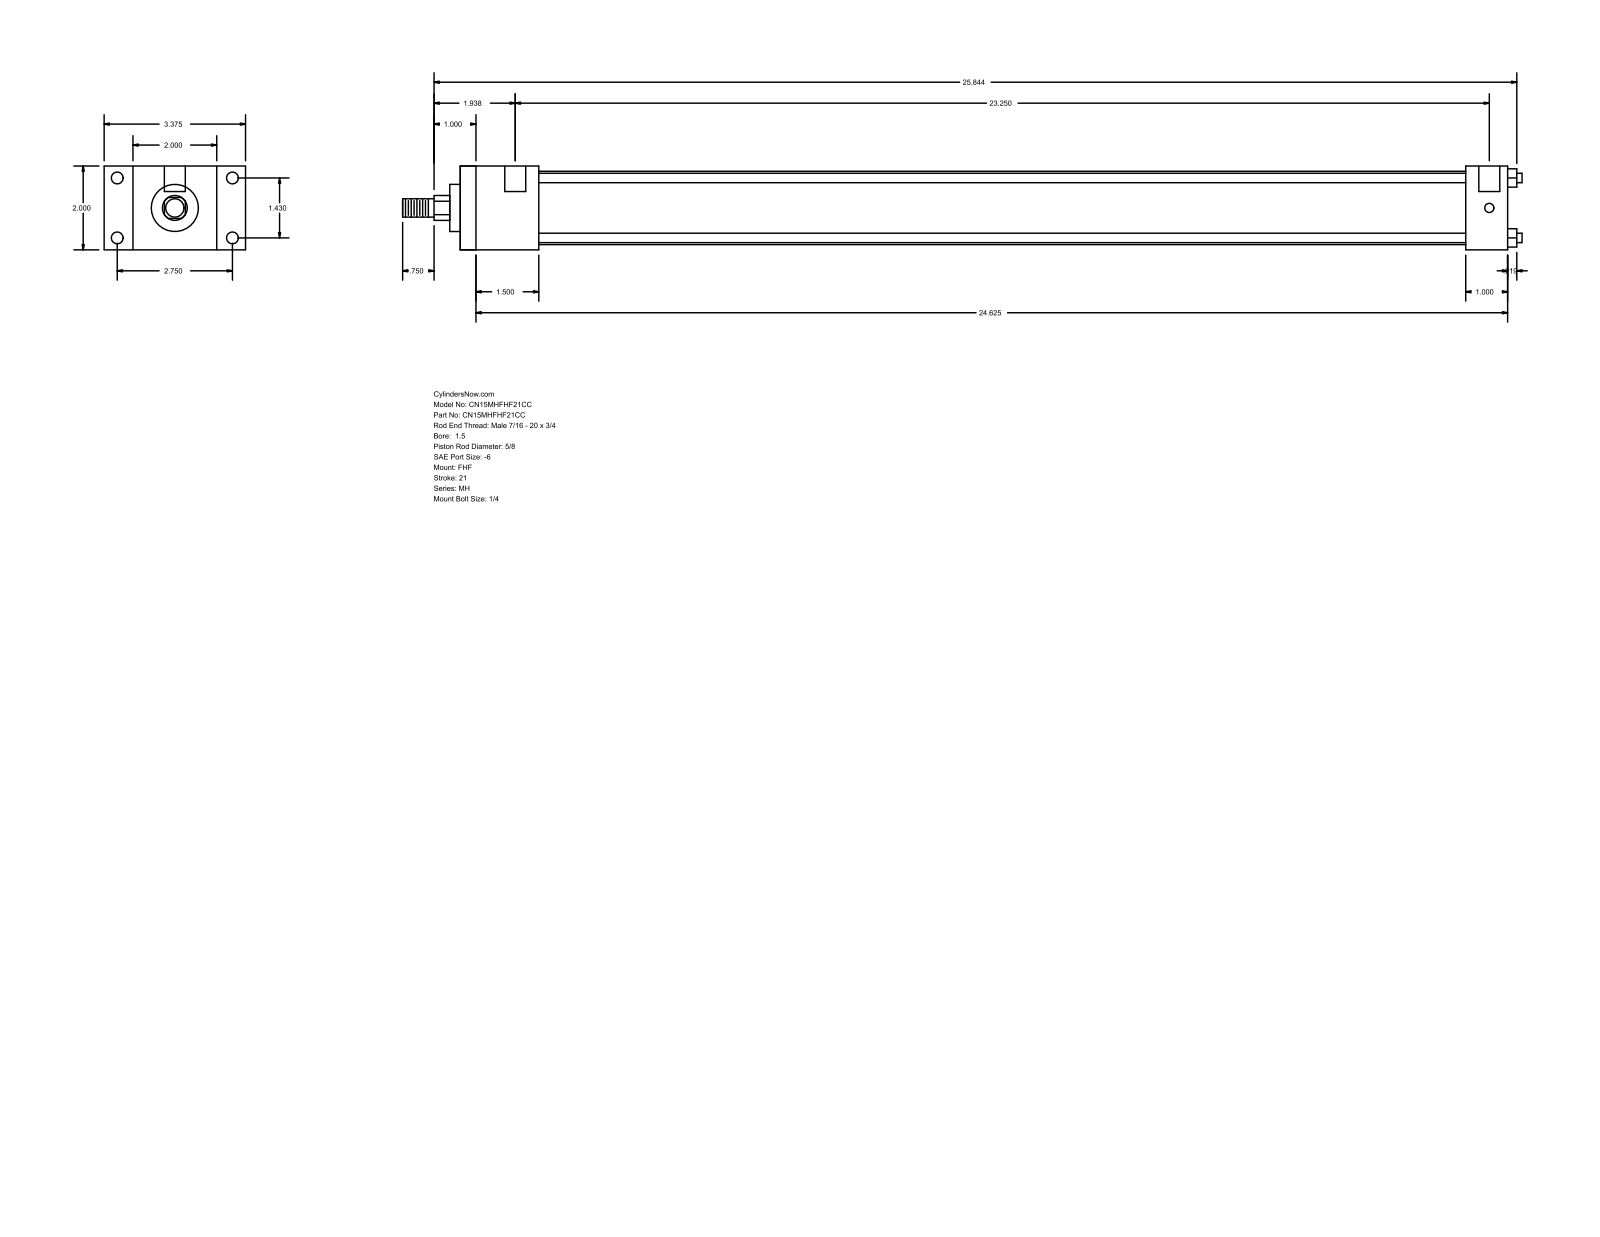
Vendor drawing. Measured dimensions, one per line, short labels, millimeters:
name: MH_FHF__0150_0.625
written by: GSSL Pune (CONFIG_CONTROL_DESIGN)
unit: mm
bodies: 0 solids, 88 faces (60 planar, 28 cylindrical, 0 other)
size: 678.66 × 85.72 × 50.8
holes: 4× ⌀5.56, 4× ⌀7.14, 2× ⌀12.7
bosses: 4× ⌀5.71, 1× ⌀44.45, 1× ⌀28.57, 1× ⌀15.88, 1× ⌀11.11
rounds: 1× R7.54
face distances: 50.8, 17.46, 68.26, 47.62, 85.72, 635, 587.38, 25.4, 609.6, 561.98
hole spacings: 36.32, 69.84, 78.72, 593.72, 3.17, 590.55
